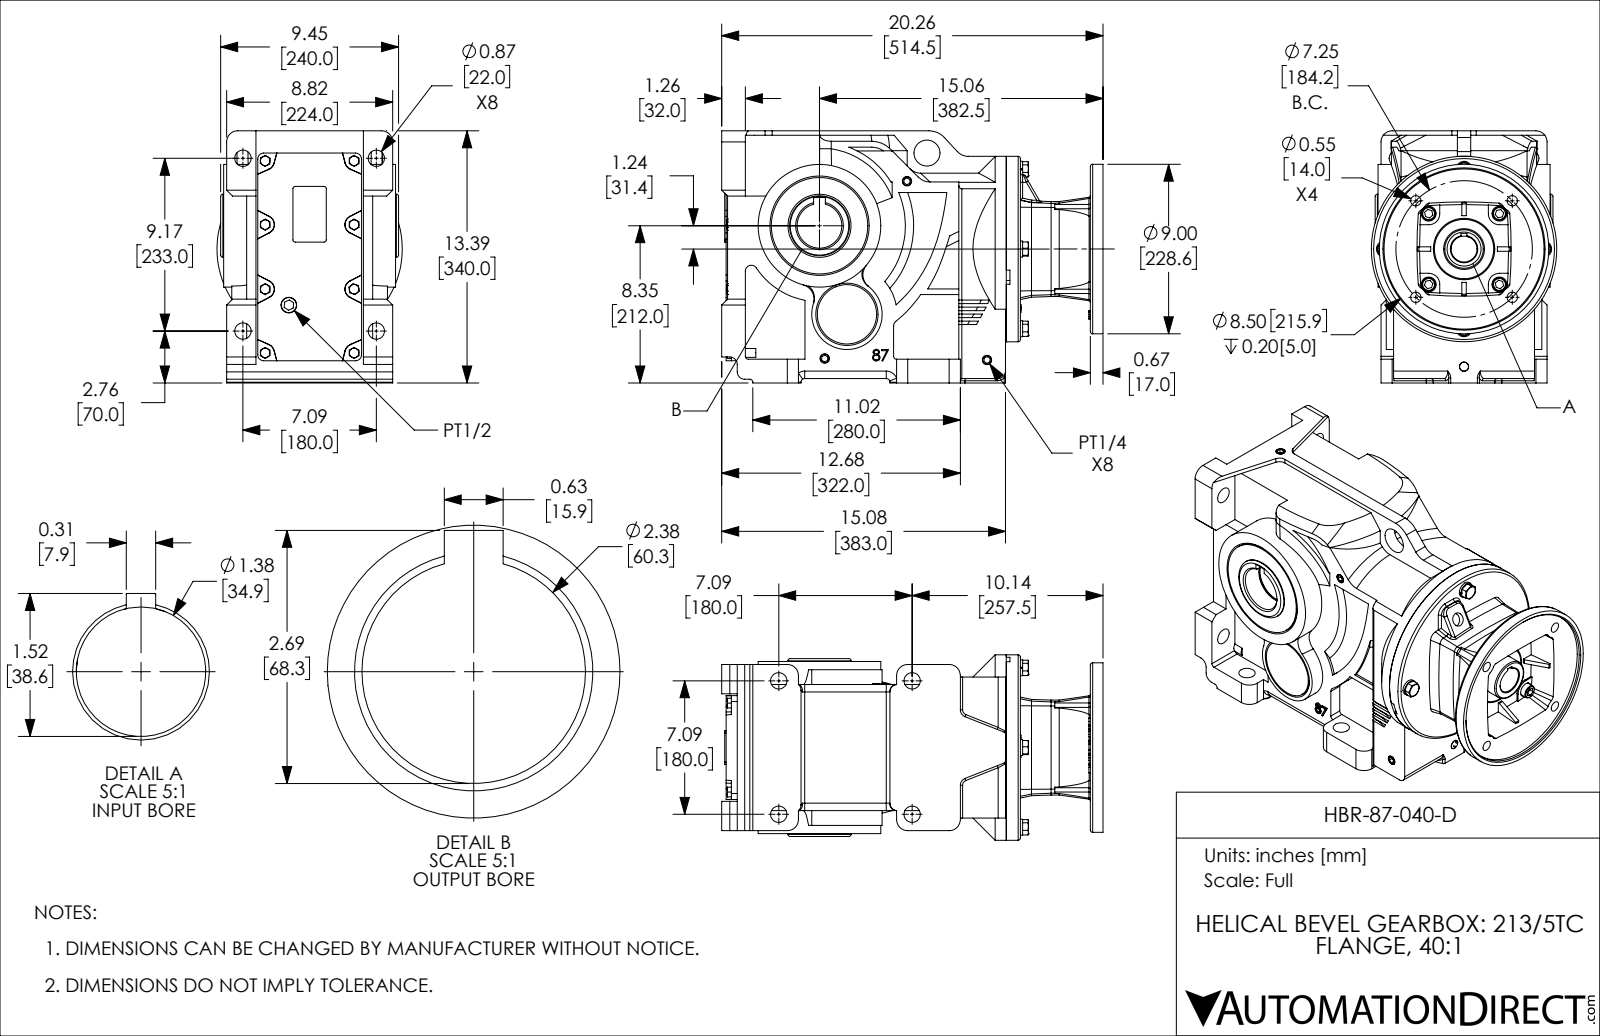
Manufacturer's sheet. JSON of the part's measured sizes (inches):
{"part_name": "HBR-87-040-D", "step_written_by": "SolidWorks 2018 (AUTOMOTIVE_DESIGN)", "units": "inches", "bodies": {"solids": 9, "faces": 1185, "planar": 575, "cylindrical": 309, "other": 301}, "overall_size": [20.256, 13.501, 9.843], "volume_in3": 1441, "surface_area_in2": 1528, "round_holes": [[0.551, 8], [0.866, 8], [0.48, 4], [0.496, 4], [0.787, 4], [0.473, 1], [0.709, 1], [0.827, 1], [1.125, 1], [1.376, 1], [1.378, 1], [1.417, 1]], "round_bosses_or_shafts": [[0.846, 4], [0.709, 4], [0.472, 4], [3.15, 2], [9.843, 1], [9, 1], [6.513, 1], [5.118, 1]], "partial_cylinders_radius": [[0.591, 22], [0.394, 17], [0.118, 15], [0.157, 7], [0.315, 6], [0.008, 4], [0.236, 4], [0.472, 4]], "face_to_face_distances": [0.669, 0.236, 6.024, 1.063, 7.087, 13.15, 0.394, 14.882, 1.22, 1.89], "hole_center_spacings": [3.011, 6.394, 4.495, 7.087, 7.263, 2.657, 3.059, 3.758]}
